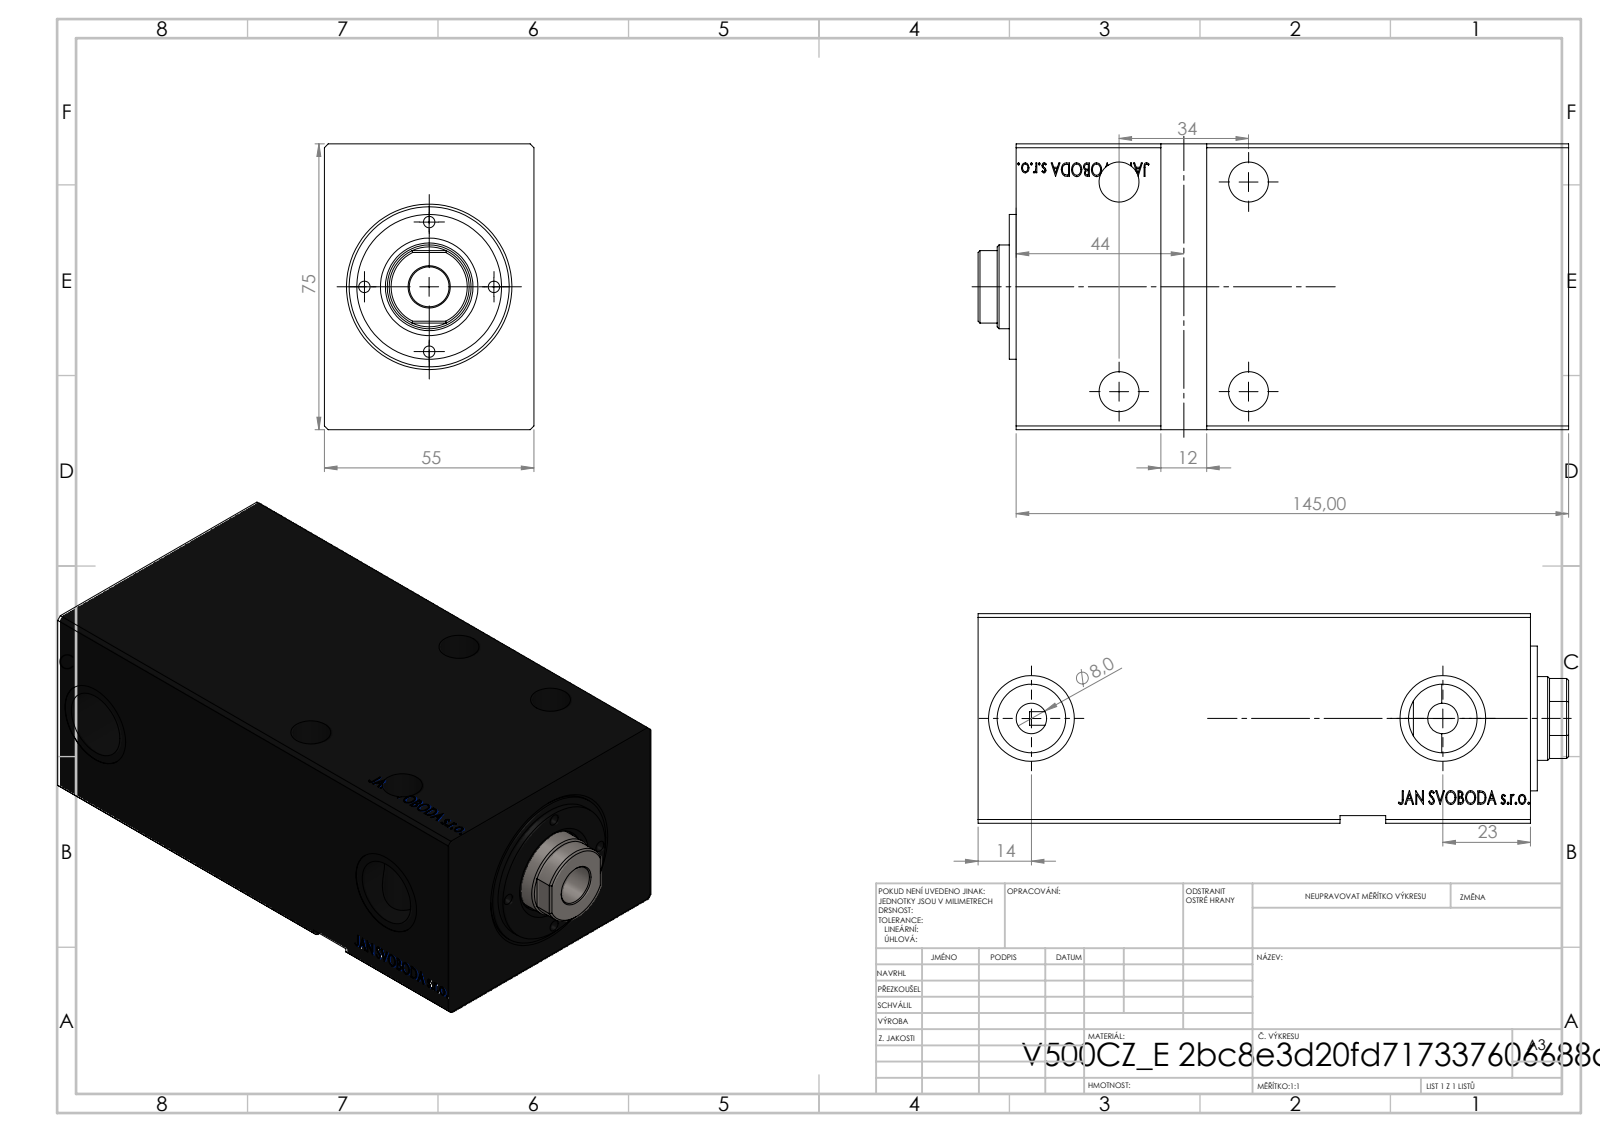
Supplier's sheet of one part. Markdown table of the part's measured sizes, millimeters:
| quantity | value |
| --- | --- |
| STEP written by | SolidWorks 2019 (CONFIG_CONTROL_DESIGN) |
| units | millimeters |
| bodies | 1 solid, 751 faces (367 planar, 32 cylindrical, 352 other) |
| overall size | 145 × 75 × 55 |
| volume | 458 780 mm³ |
| surface area | 67 265 mm² |
| round holes (diameter × count) | 8 × 4, 10.5 × 4, 18 × 2, 22.5 × 2, 32 × 1, 36 × 1, 42 × 1 |
| main face-to-face distances | 55, 75, 145, 13.6, 144.8, 2, 53, 131.2, 13.8, 10 |
| hole center spacings | 34, 55, 64.66, 18.5, 33.02, 37.98, 46.8, 62.5 |
